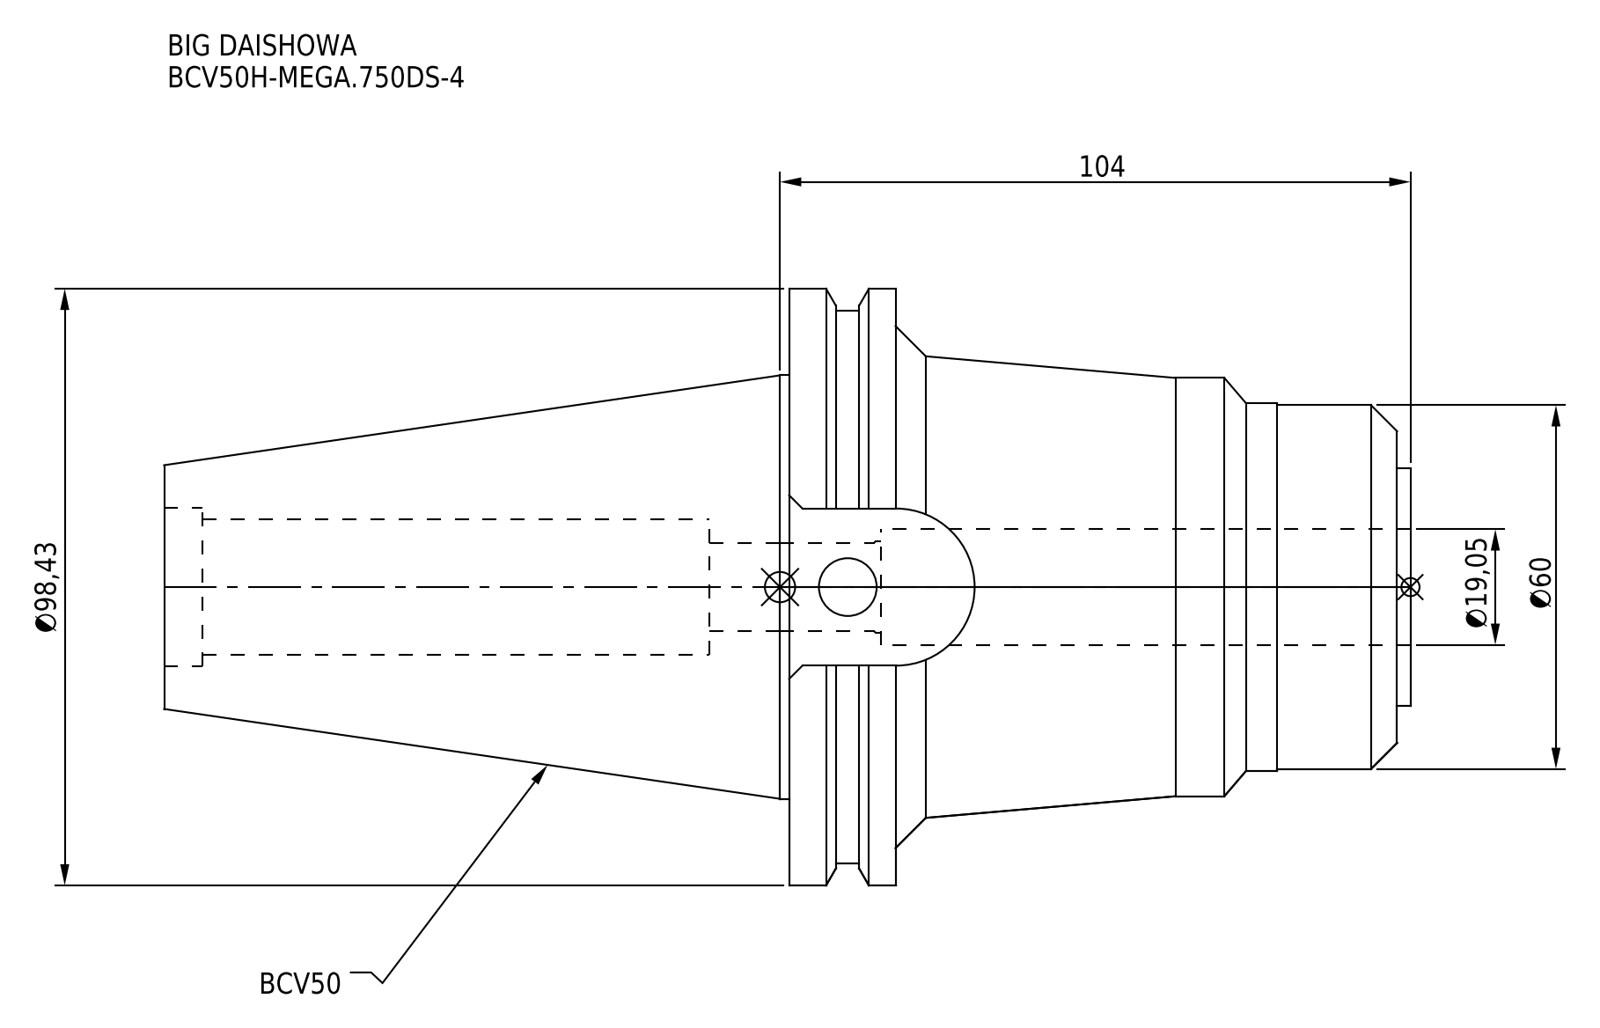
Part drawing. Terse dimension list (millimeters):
name: BCV50H-MEGA_750DS-4
written by: CREO PARAMETRIC BY PTC INC, 2016380 (AUTOMOTIVE_DESIGN)
unit: mm
bodies: 1 solid, 73 faces (26 planar, 33 cylindrical, 14 other)
size: 205.6 × 98.42 × 94.95
volume: 614 441 mm³; area: 65 098 mm²
holes: 1× ⌀9.53, 1× ⌀14.5, 1× ⌀15, 1× ⌀19.05, 1× ⌀22.3, 1× ⌀26.23
bosses: 1× ⌀98.42, 1× ⌀91.29, 1× ⌀69.85, 1× ⌀69, 1× ⌀60.7, 1× ⌀60, 1× ⌀39.3
rounds: 1× R12.96
face distances: 17.55, 84.95, 102.5, 2.2, 82.75, 100.3, 205.6, 203.4, 120.65, 103.1
